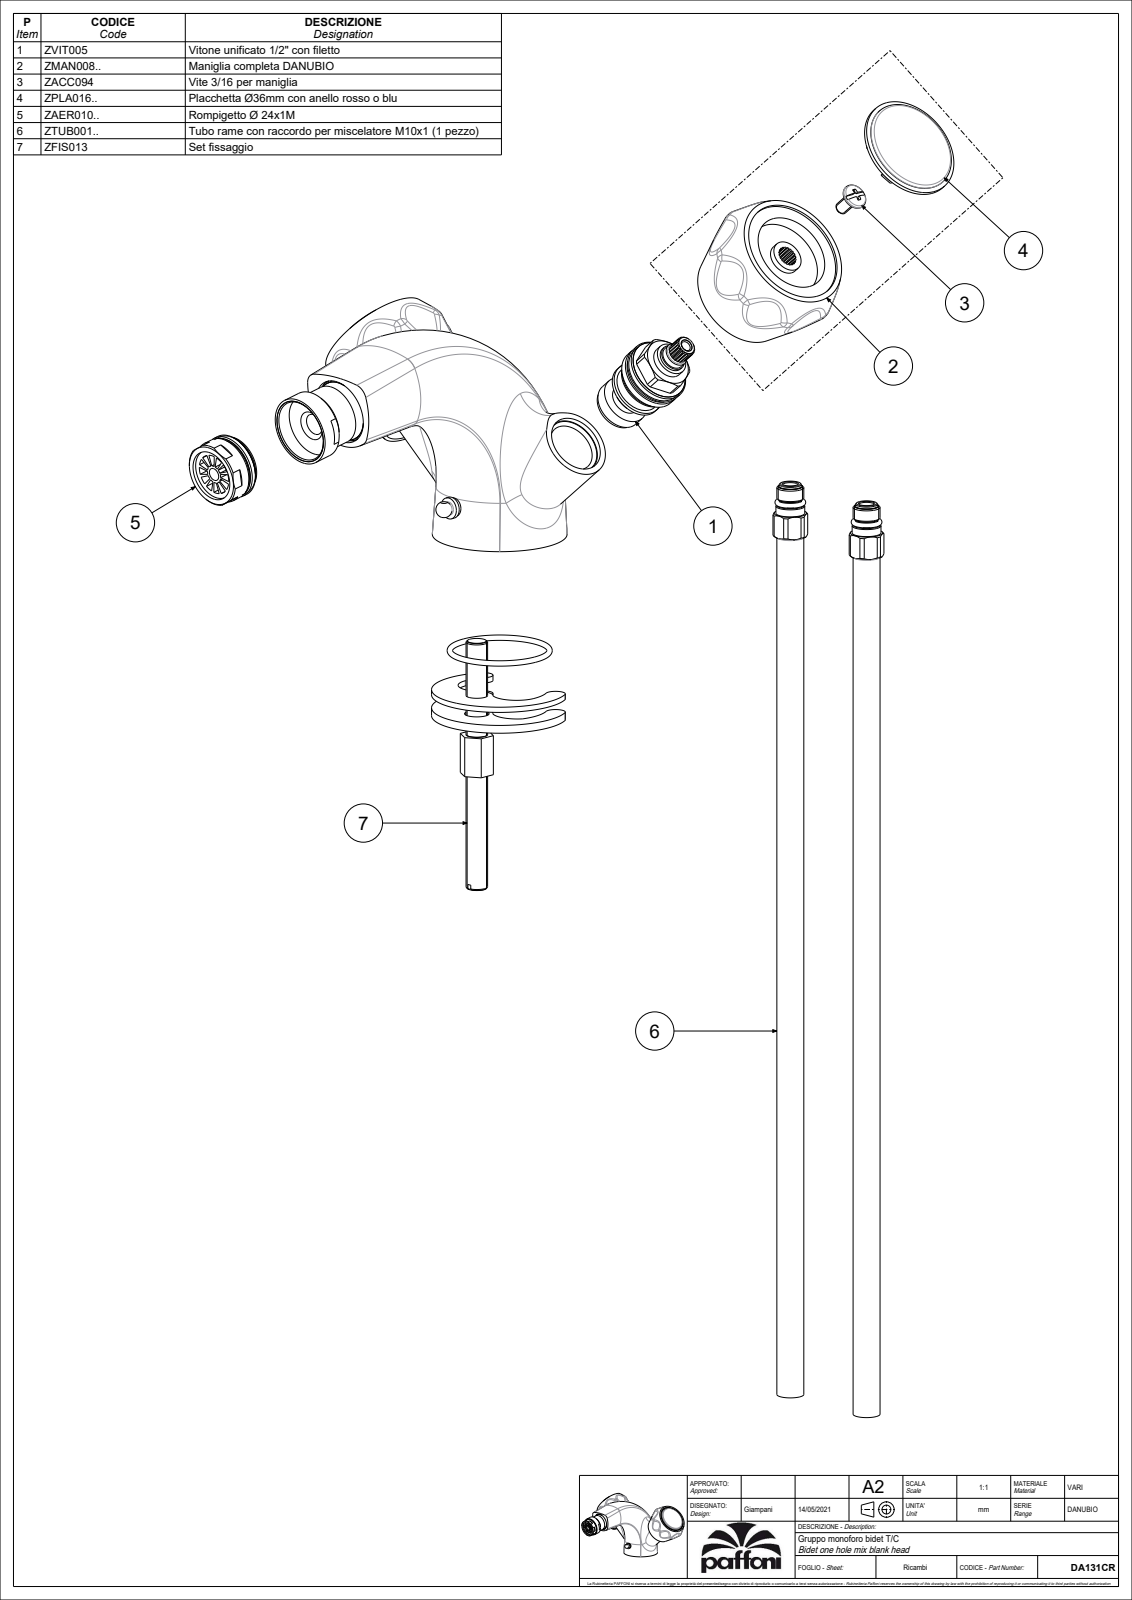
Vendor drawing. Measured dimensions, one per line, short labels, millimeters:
name: DA131CR
written by: CREO PARAMETRIC BY PTC INC, 2020044 (CONFIG_CONTROL_DESIGN)
unit: mm
bodies: 1 solid, 224 faces (30 planar, 34 cylindrical, 160 other)
size: 159.12 × 138.85 × 85.43
volume: 331 658 mm³; area: 39 908 mm²
bosses: 2× ⌀38.5, 1× ⌀25.8, 1× ⌀23.8, 1× ⌀22.5, 1× ⌀10, 1× ⌀8, 1× ⌀4.5
rounds: 16× R21.31, 2× R13
face distances: 35.31, 35.71, 0.4, 28.31, 25.31, 3, 7.31, 18, 21, 22.9
